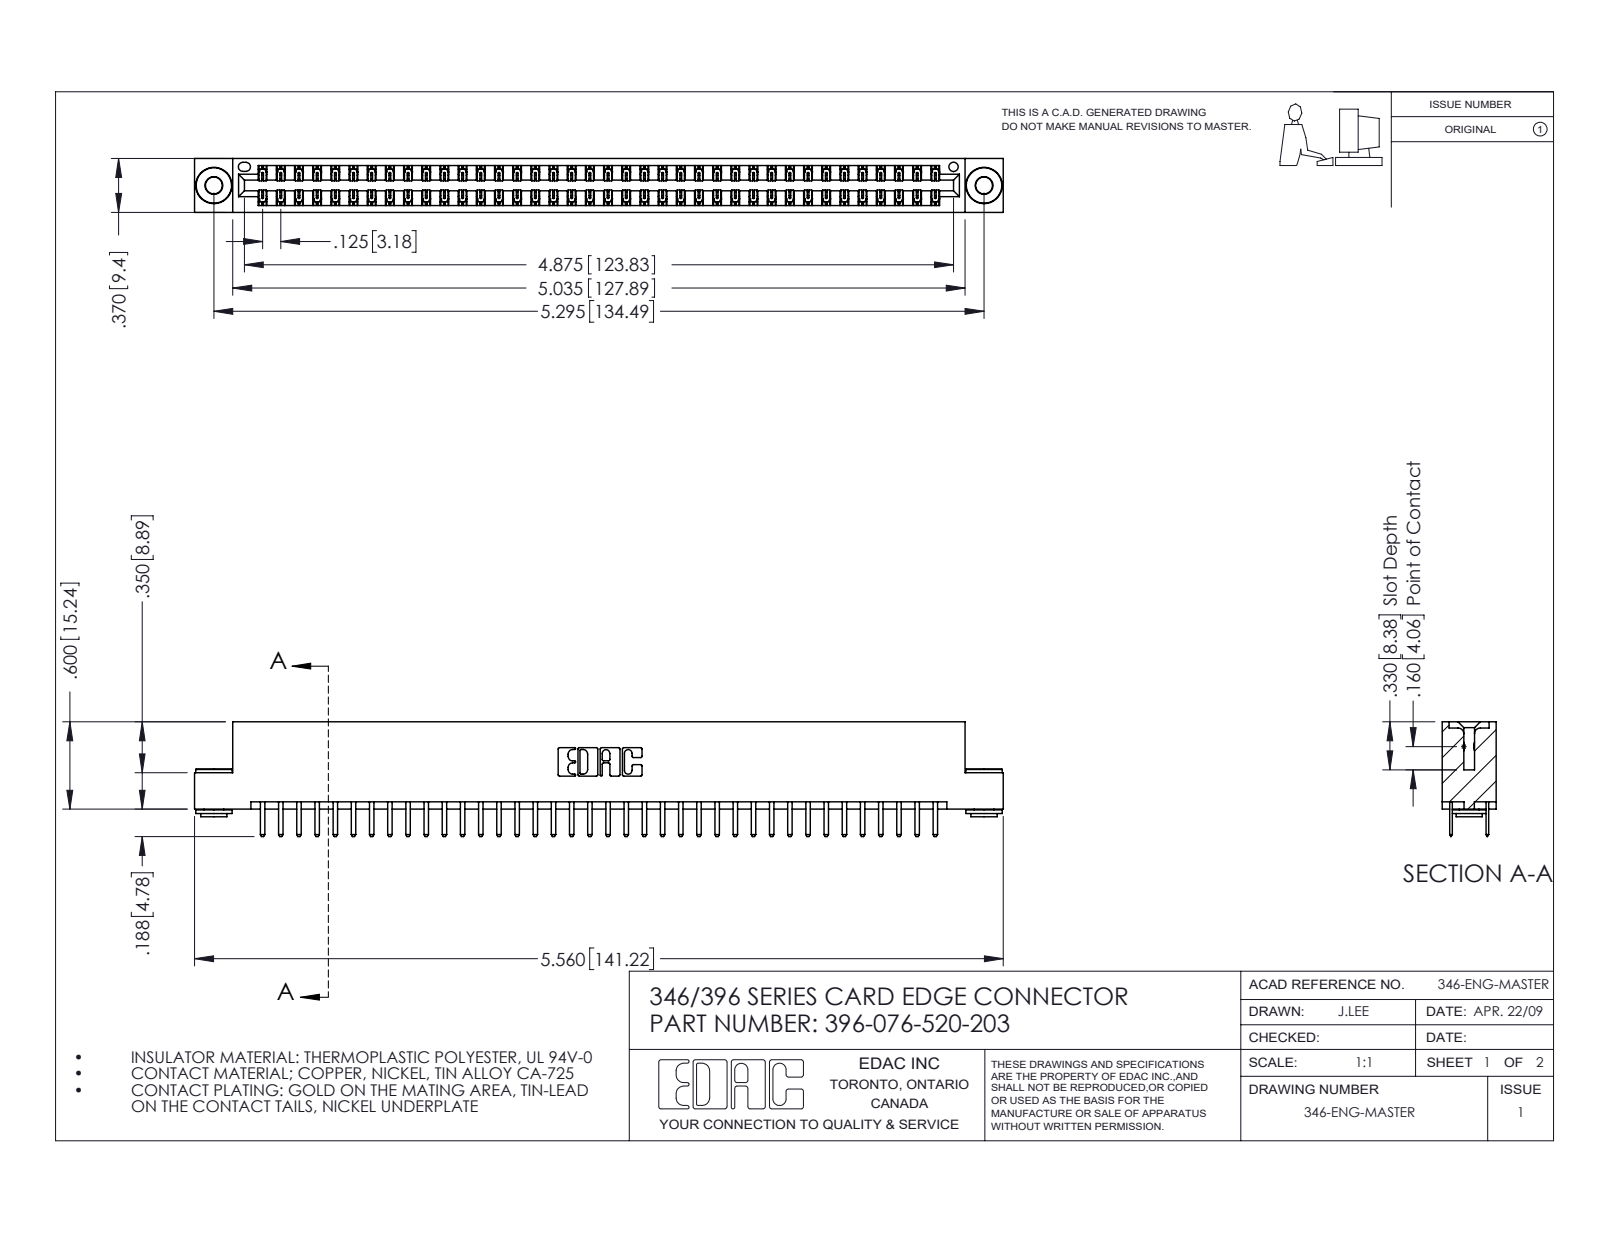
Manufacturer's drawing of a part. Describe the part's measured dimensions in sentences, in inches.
The part is named "346 Part_Flush Mounting Lugs - 0.156 Dia-TH; 345-292-001_345-293-120; 345-250-002_345-250-002-102; 396-076-520-203". Its 3-D file was written by "SolidWorks 2016 (CONFIG_CONTROL_DESIGN)". It is 79 solids with 4416 faces: 2898 planar, 1510 cylindrical and 8 other. Overall it measures 5.56 by 0.788 by 0.37 inches. Its volume is 0.838 cubic inches and its surface area 29.36 square inches. Round holes: 2 of diameter 0.116, 2 of diameter 0.156, 1 of diameter 0.064. Round bosses or shafts: 2 of diameter 0.25, 2 of diameter 0.18, 2 of diameter 0.136. Partial cylindrical surfaces (rounded edges, fillets, slot ends): 114 of radius 0.006, 80 of radius 0.01, 22 of radius 0.01, 6 of radius 0.007, 6 of radius 0.031, 3 of radius 0.026, 2 of radius 0.014, 2 of radius 0.022. The main face-to-face distances are 0.048, 0.322, 0.25, 0.37, 0.025, 0.275, 0.072, 0.298, 0.148, 0.222. The hole center spacings are 0.246, 5.086, 5.295.
